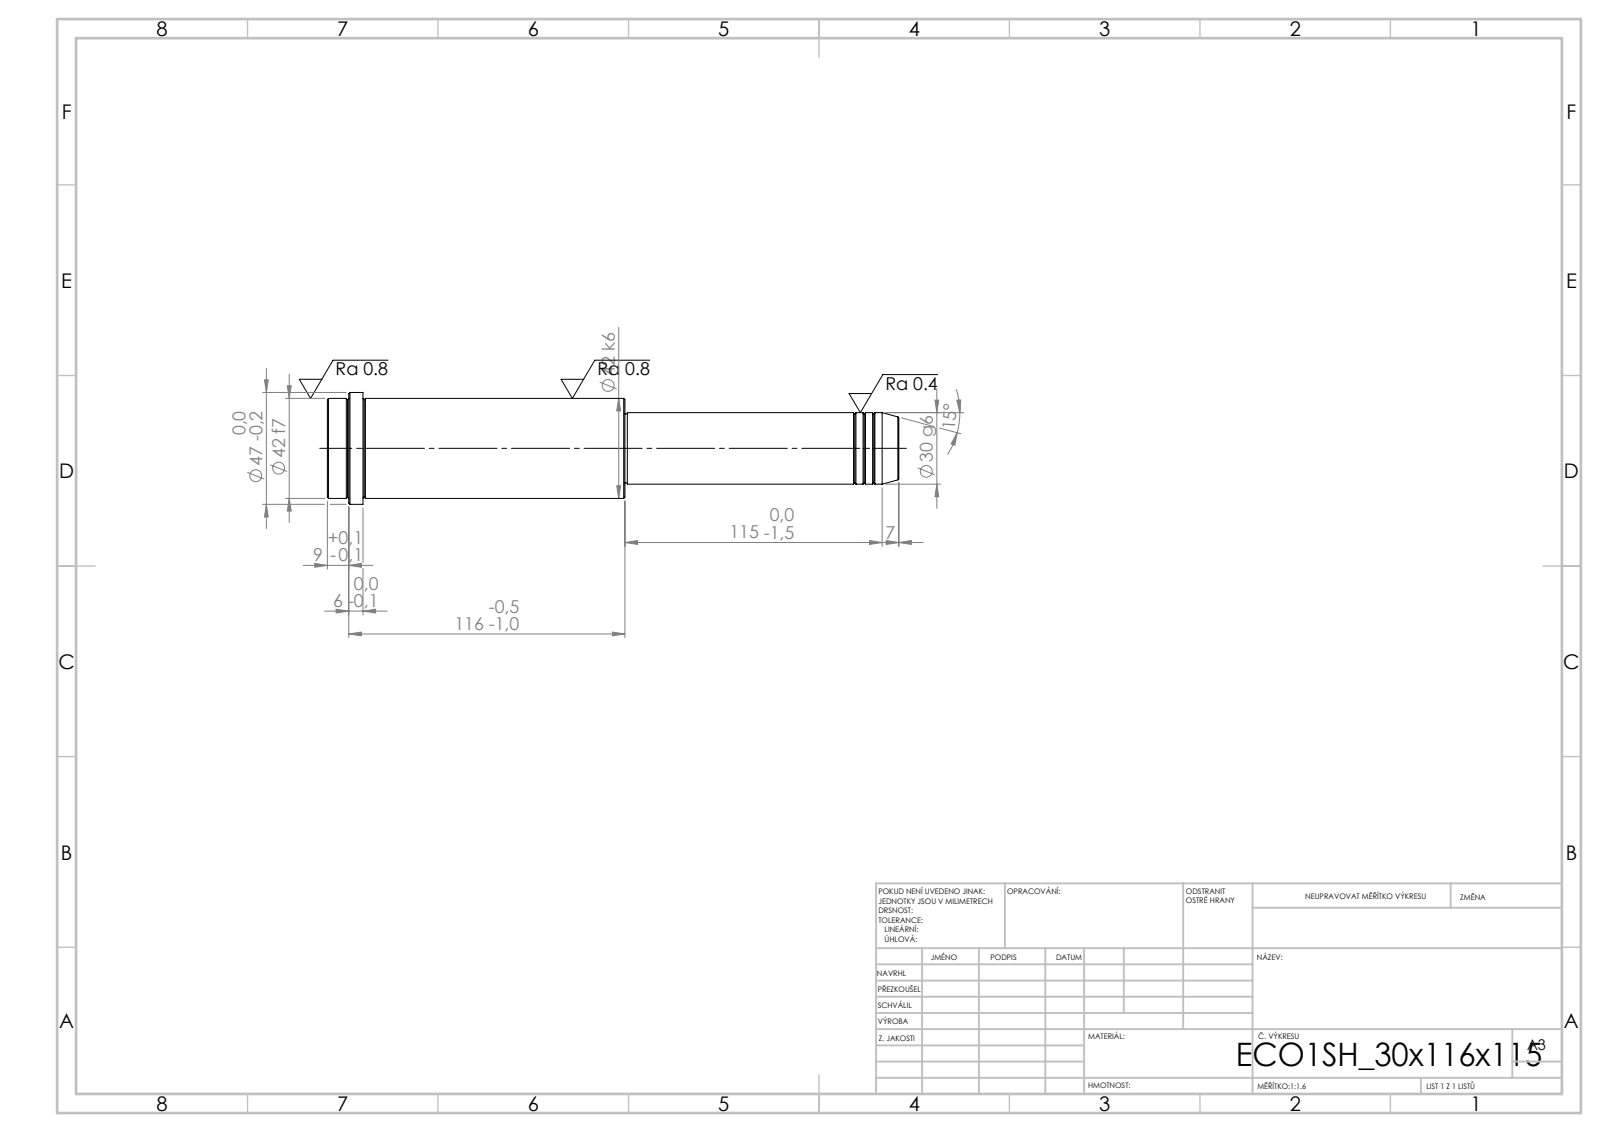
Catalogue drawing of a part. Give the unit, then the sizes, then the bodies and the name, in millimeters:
Units: millimetres
Overall size (bounding box): 240 × 47 × 47
Round bosses / shafts (diameter × count): ⌀47 ×1, ⌀42 ×1, ⌀30 ×1, ⌀29 ×1
Main face-to-face distances: 125, 115, 240, 225, 110, 15, 231, 116, 6, 9
Volume: 255 661 mm³ · Surface area: 30 966 mm²
Bodies: 1 solid, 52 faces (6 planar, 16 cylindrical, 30 other)
STEP written by: SolidWorks 2019 (CONFIG_CONTROL_DESIGN)
